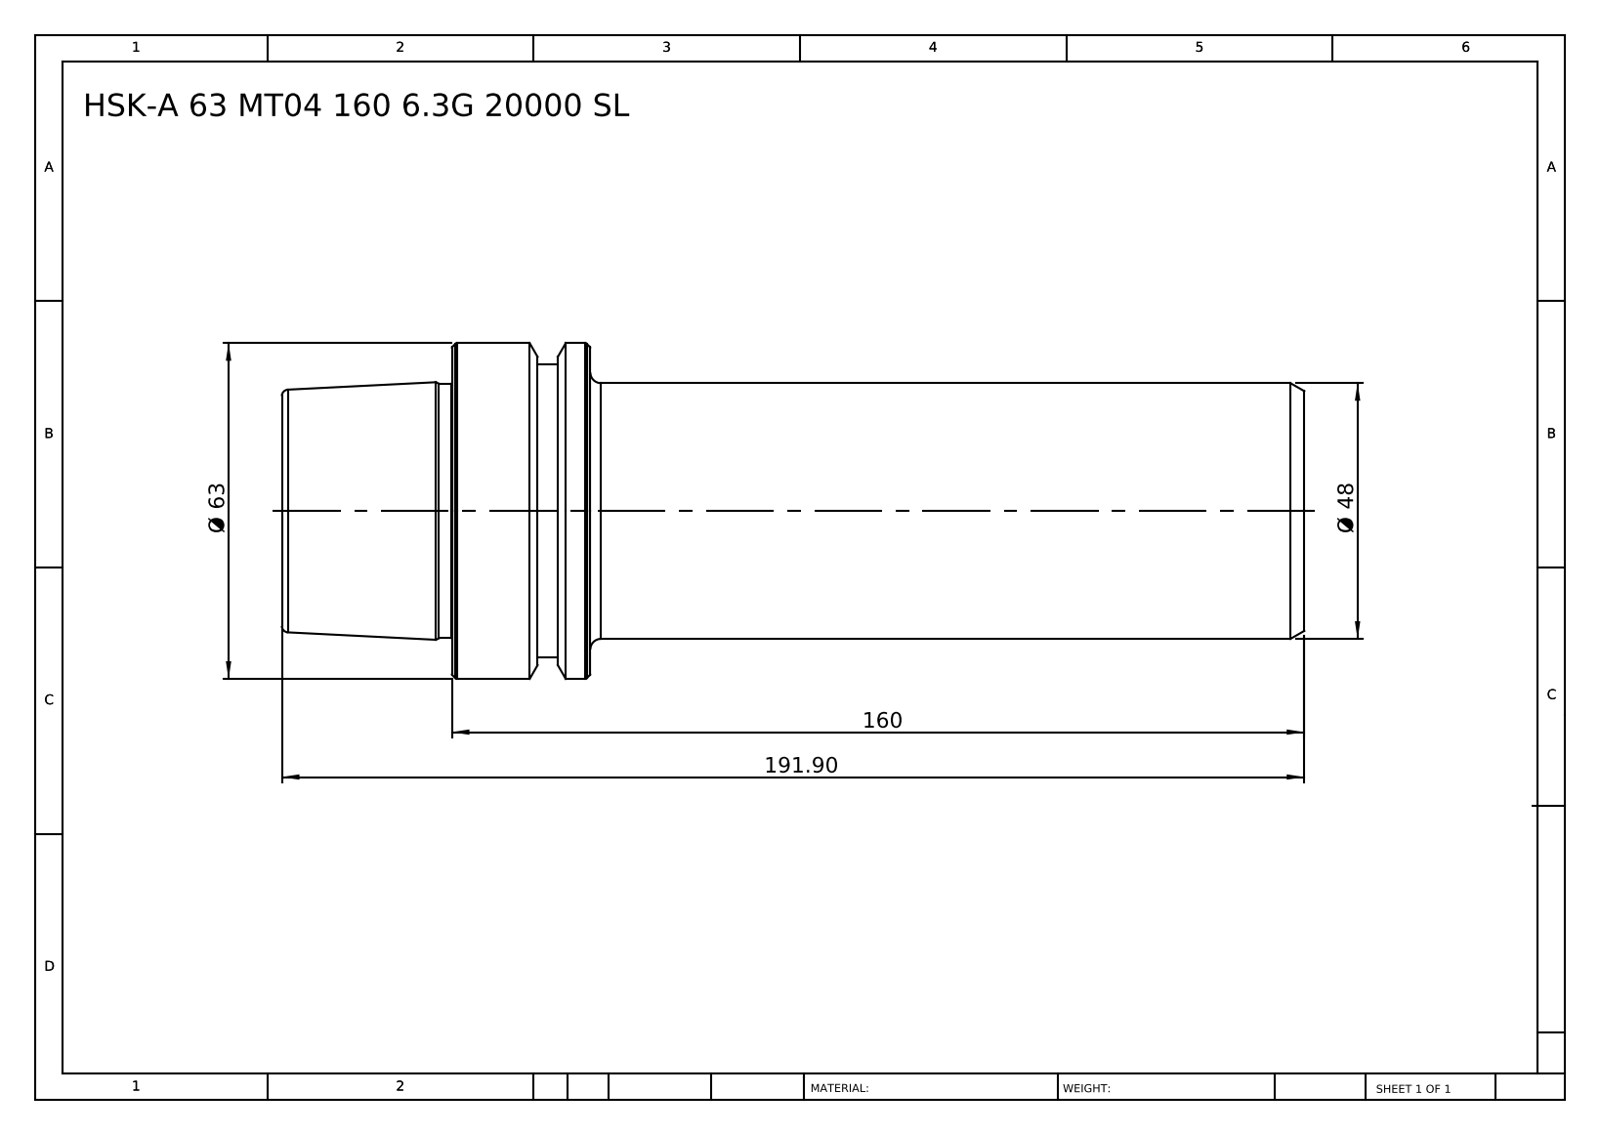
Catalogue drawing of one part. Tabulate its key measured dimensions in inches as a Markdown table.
| quantity | value |
| --- | --- |
| part name | HSK-A 63 MT04 160 6.3G 20000 SL |
| STEP written by | SolidWorks 2014 (CONFIG_CONTROL_DESIGN) |
| units | inches |
| bodies | 1 solid, 46 faces (6 planar, 10 cylindrical, 30 other) |
| overall size | 7.555 × 2.48 × 2.48 |
| volume | 22.88 in³ |
| surface area | 56.66 in² |
| round bosses / shafts (diameter × count) | 2.48 × 1, 2.165 × 1, 1.89 × 1, 1.881 × 1 |
| main face-to-face distances | 7.555, 5.276, 2.28, 6.299, 1.024, 1.256, 5.516, 0.24, 0.783, 2.039 |
